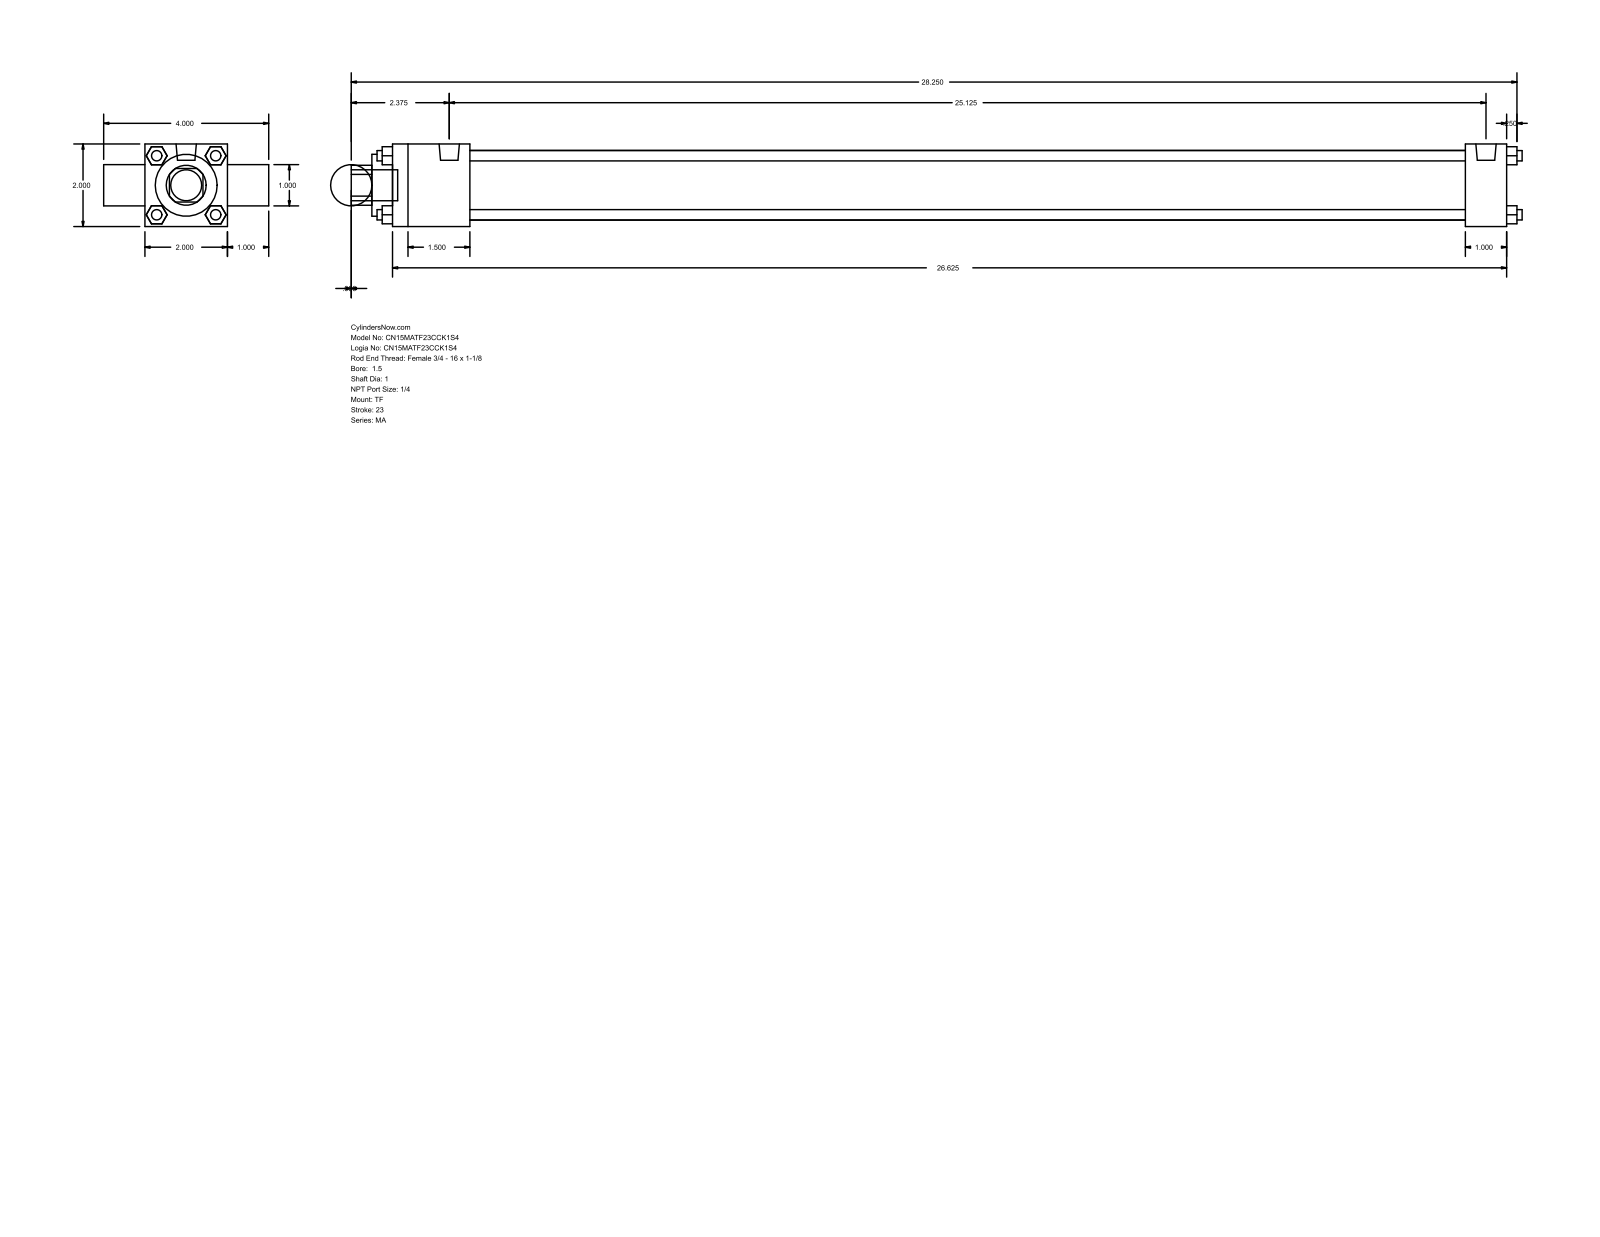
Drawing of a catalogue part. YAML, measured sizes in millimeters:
part_name: "MA_TF__0150_1"
step_written_by: "GSSL Pune (CONFIG_CONTROL_DESIGN)"
units: millimeters
bodies: {solids: 0, faces: 120, planar: 92, cylindrical: 28, other: 0}
overall_size: [720.73, 101.6, 50.8]
round_holes:
  - {diameter: 25.4, count: 2}
  - {diameter: 38.1, count: 1}
  - {diameter: 42.93, count: 1}
round_bosses_or_shafts:
  - {diameter: 6.35, count: 4}
  - {diameter: 7.94, count: 3}
  - {diameter: 12.49, count: 2}
  - {diameter: 19.05, count: 1}
partial_cylinders:
  - {radius: 12.29, count: 1}
face_to_face_distances: [50.8, 25.4, 685.8, 76.2, 6.35, 47.63, 660.4, 612.77, 638.17, 698.5]
